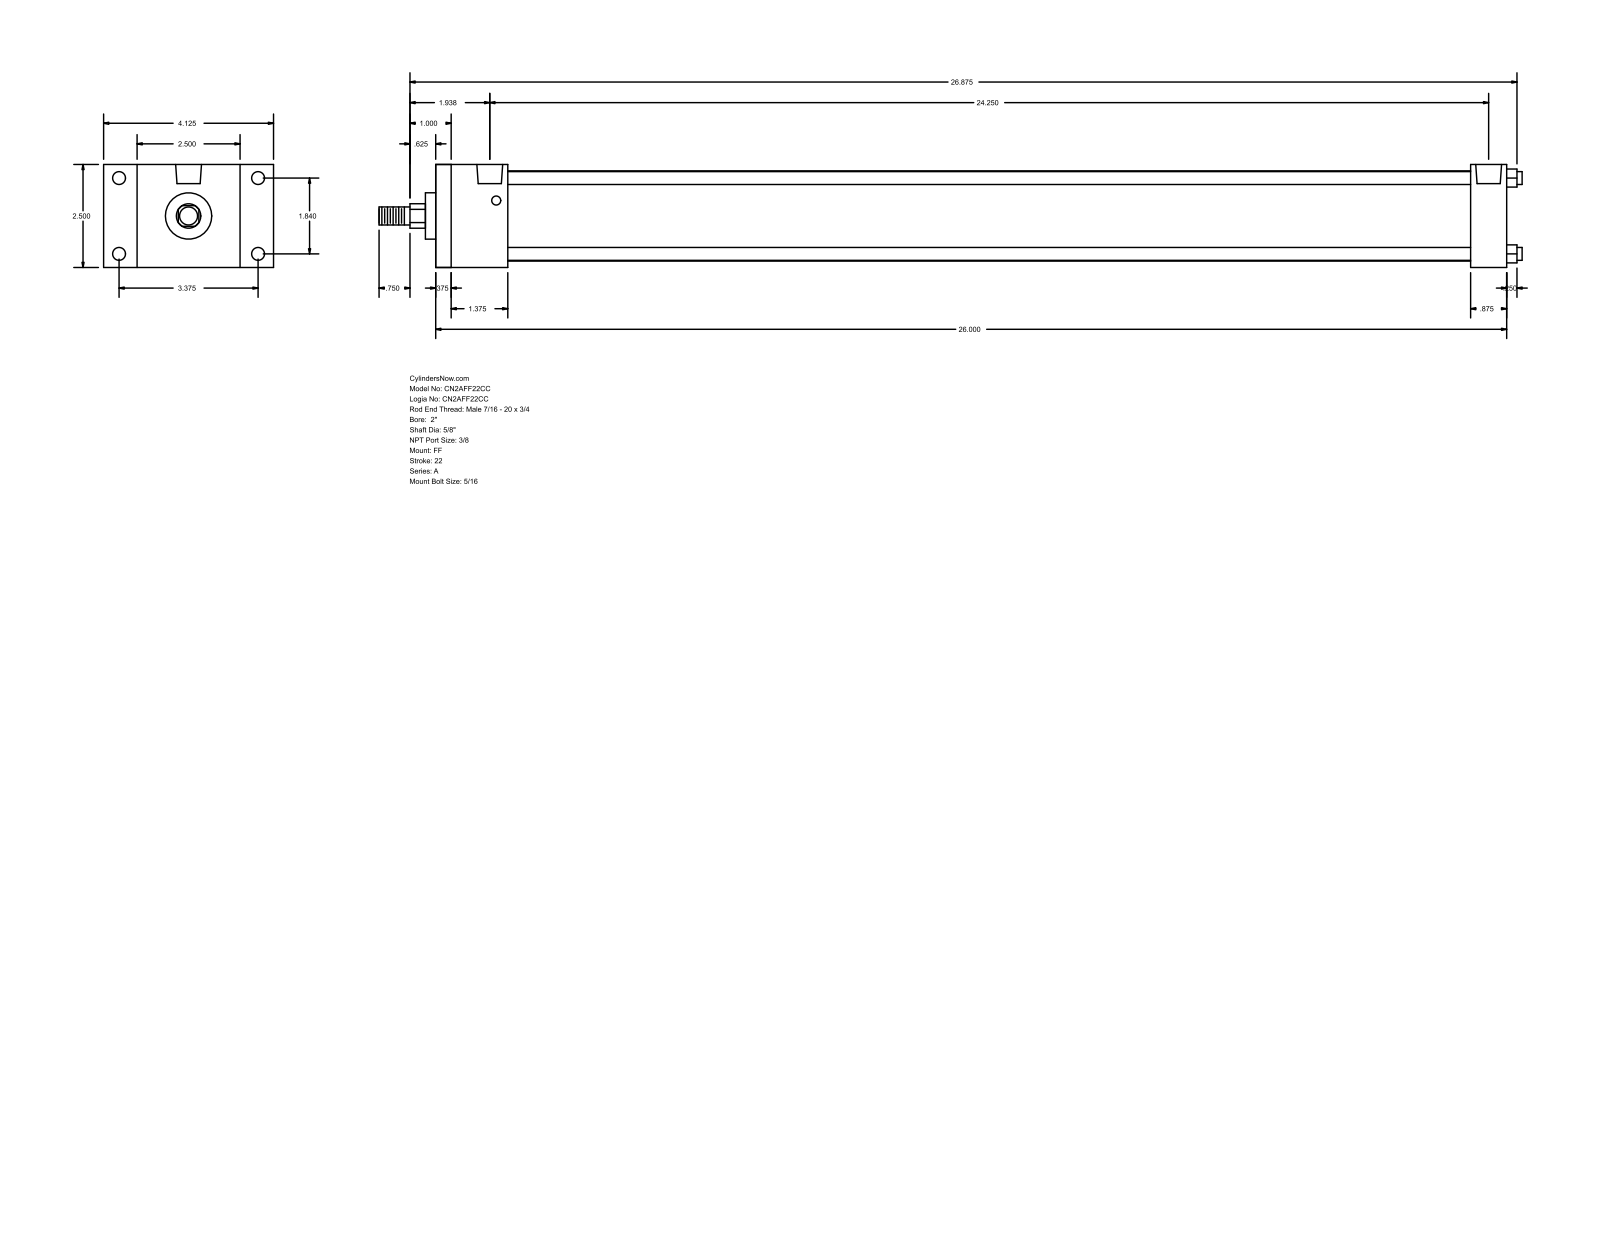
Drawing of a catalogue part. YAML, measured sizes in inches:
part_name: "A_FF__0200_0.625"
step_written_by: "GSSL Pune (CONFIG_CONTROL_DESIGN)"
units: inches
bodies: {solids: 0, faces: 92, planar: 64, cylindrical: 28, other: 0}
overall_size: [27.75, 4.125, 2.5]
round_holes:
  - {diameter: 0.219, count: 4}
  - {diameter: 0.313, count: 4}
  - {diameter: 0.627, count: 2}
round_bosses_or_shafts:
  - {diameter: 0.313, count: 4}
  - {diameter: 2.19, count: 1}
  - {diameter: 1.125, count: 1}
  - {diameter: 0.625, count: 1}
  - {diameter: 0.437, count: 1}
partial_cylinders:
  - {radius: 0.297, count: 1}
face_to_face_distances: [2.5, 26, 0.375, 25.625, 1.375, 1.75, 25.125, 24.75, 23.375, 24.25]
hole_center_spacings: [1.84, 3.375, 3.844, 23.937, 0.156, 0.157, 24.093, 24.094]
